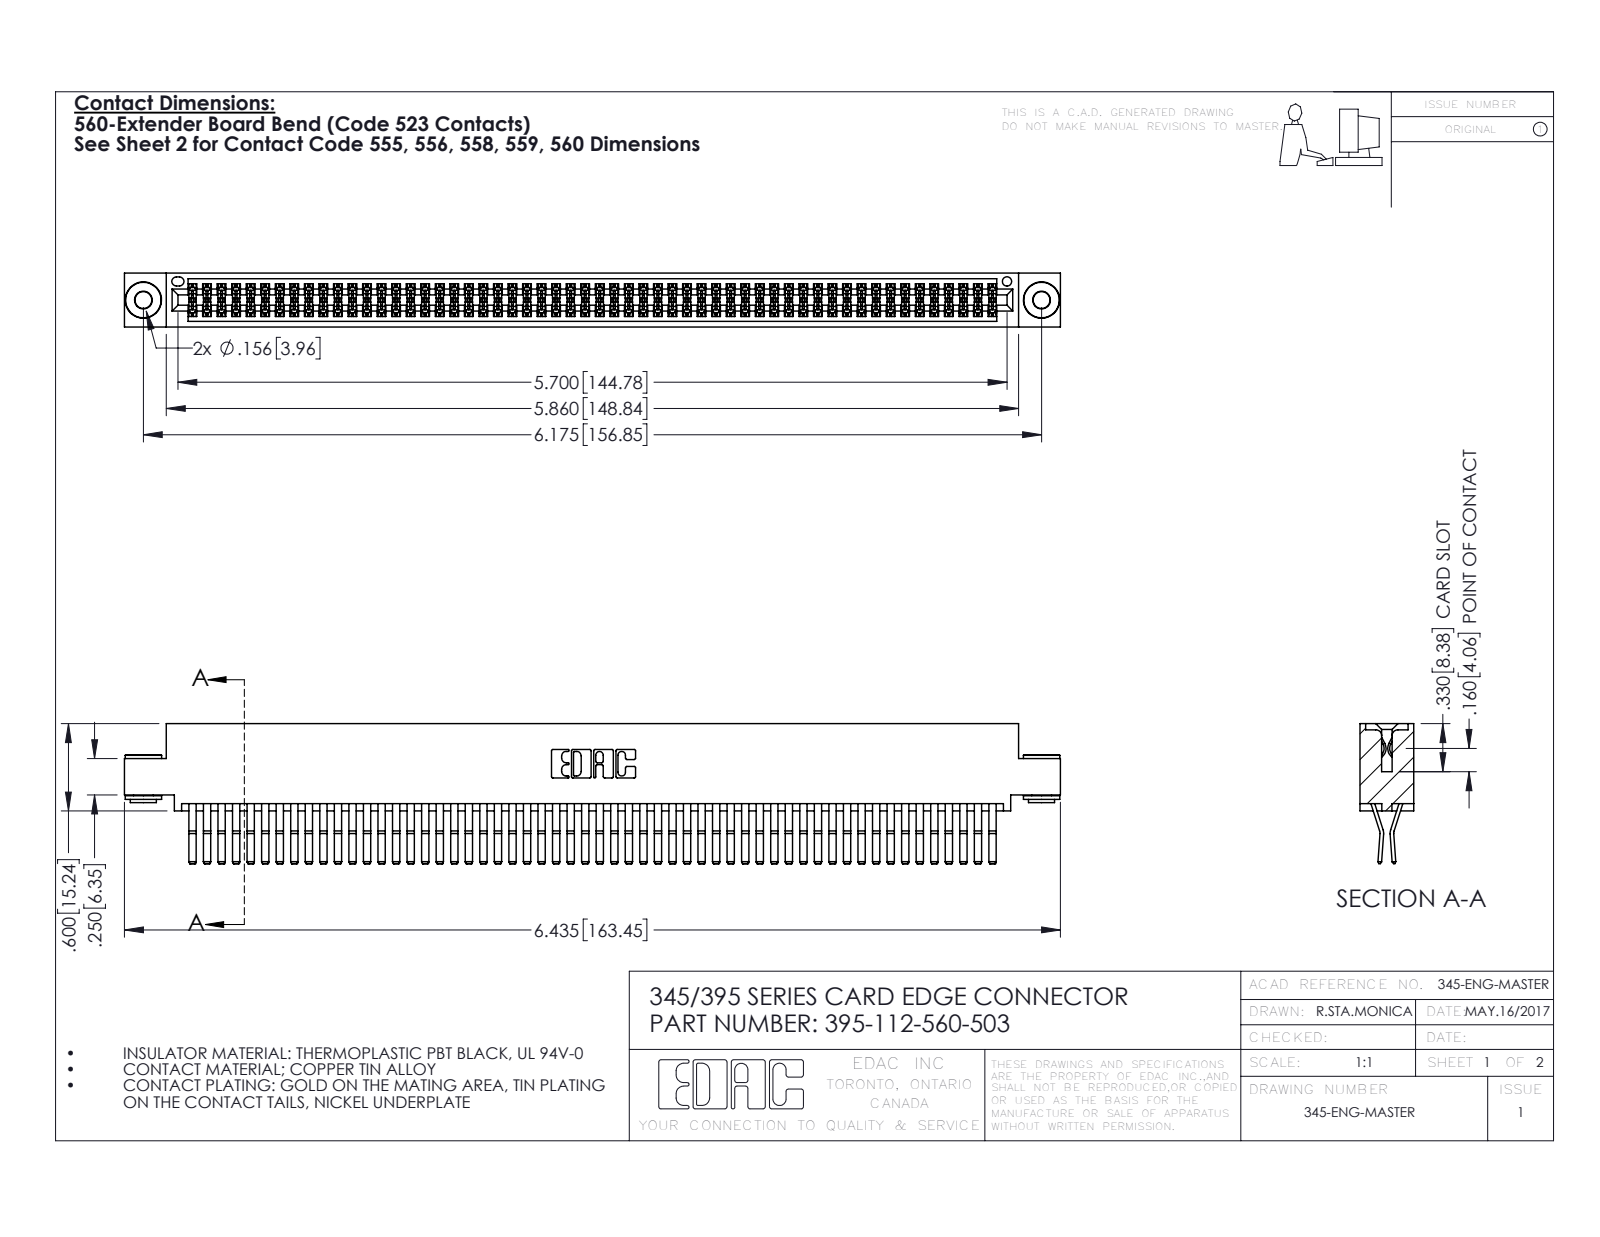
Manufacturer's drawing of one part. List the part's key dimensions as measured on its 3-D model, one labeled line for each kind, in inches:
Part name (STEP PRODUCT): 345-292-001_560 Tail; 345-250-002_345-250-002-102; 345 Part_0.110 Offset - 0.156 Dia-TH; 395-112-560-503
STEP written by: SolidWorks 2016 (CONFIG_CONTROL_DESIGN)
Units: inches
Bodies: 115 solids, 5992 faces (3790 planar, 2194 cylindrical, 8 other)
Overall size (bounding box): 6.435 × 0.962 × 0.37
Volume: 1.018 in³ · Surface area: 42.04 in²
Round holes (diameter × count): ⌀0.116 ×2, ⌀0.156 ×2, ⌀0.064 ×1
Round bosses / shafts (diameter × count): ⌀0.25 ×2, ⌀0.18 ×2, ⌀0.136 ×2
Partial cylindrical surfaces — rounded edges, fillets, slot ends (radius × count): R0.006 ×168, R0.01 ×22, R0.007 ×6, R0.031 ×6, R0.026 ×3, R0.01 ×2, R0.014 ×2, R0.019 ×2
Main face-to-face distances: 0.025, 0.072, 0.298, 0.37, 0.2, 0.098, 0.272, 0.225, 0.175, 0.149
Hole centre spacings: 0.27, 5.939, 6.175
